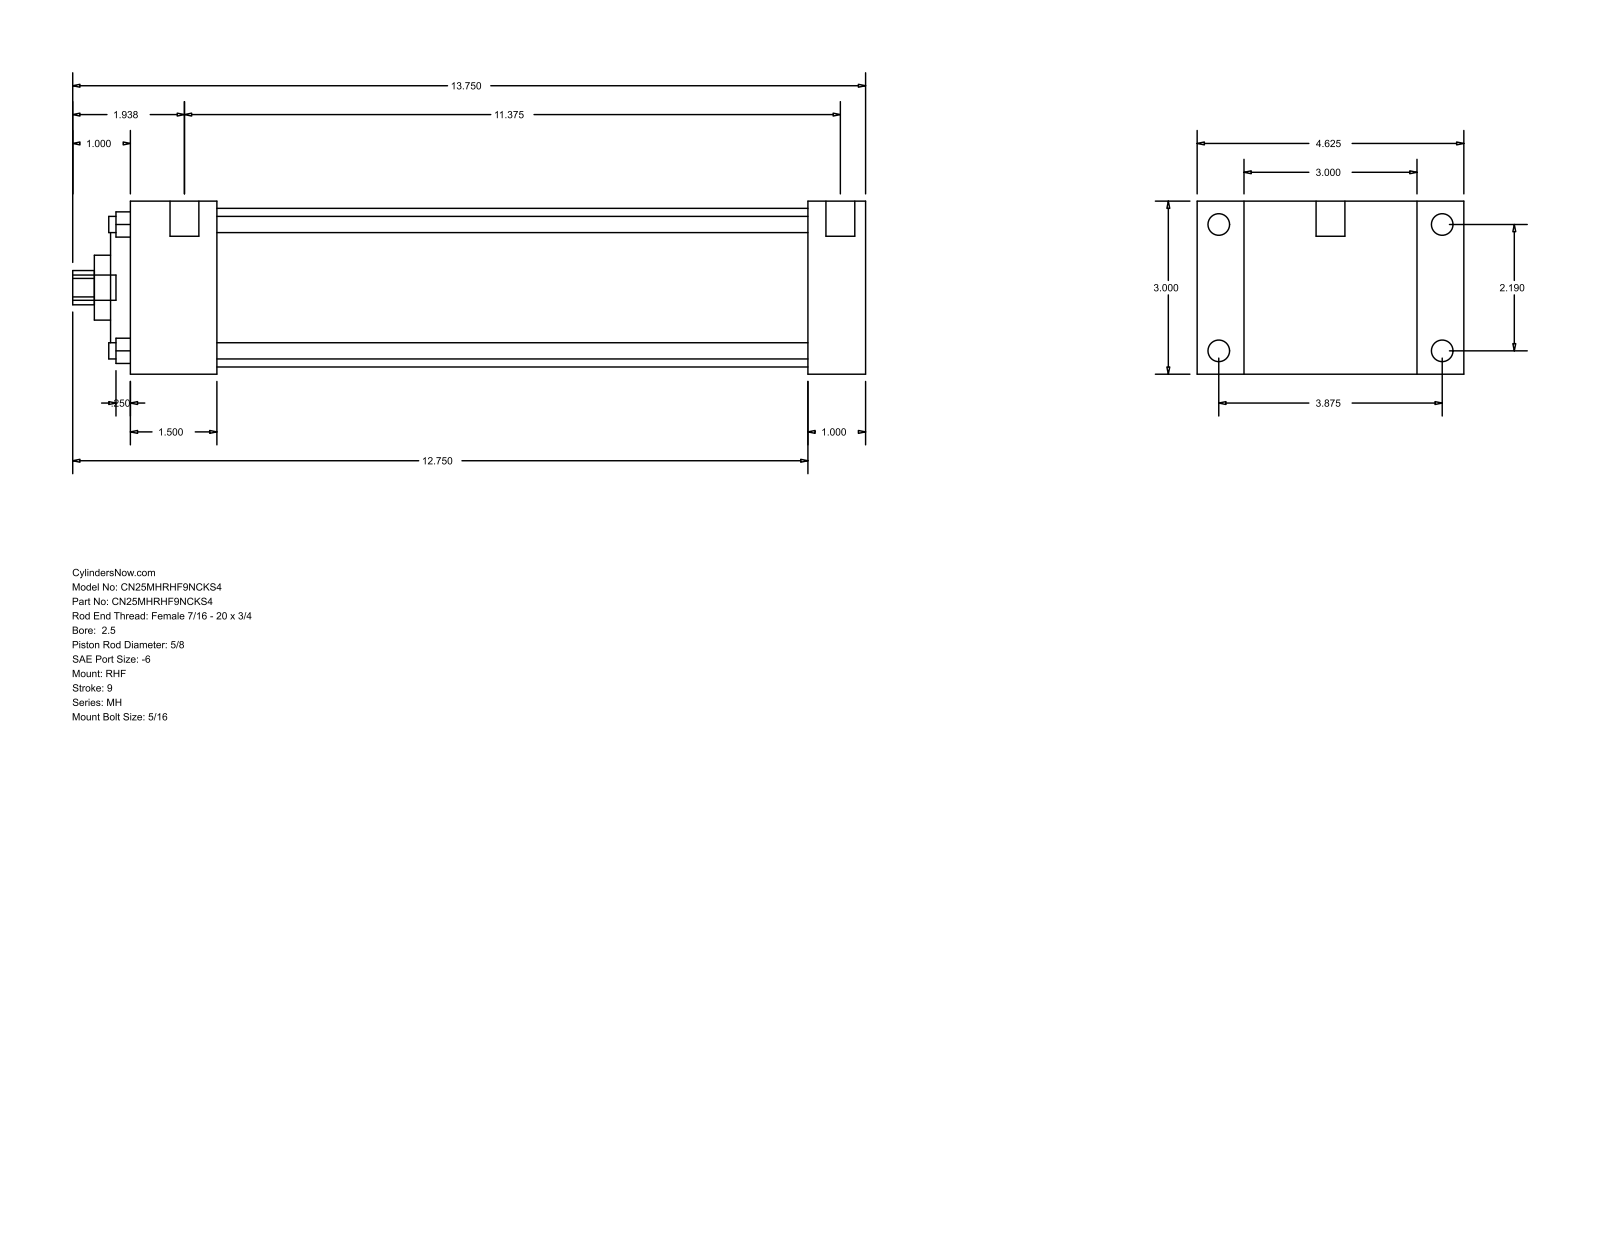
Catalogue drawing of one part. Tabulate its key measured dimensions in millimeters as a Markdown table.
| quantity | value |
| --- | --- |
| part name | MH_RHF__0250_0.625 |
| STEP written by | GSSL Pune (CONFIG_CONTROL_DESIGN) |
| units | millimeters |
| bodies | 0 solids, 90 faces (61 planar, 29 cylindrical, 0 other) |
| overall size | 349.25 × 117.47 × 76.2 |
| round holes (diameter × count) | 7.14 × 4, 15.88 × 1, 28.57 × 1, 55.55 × 1, 69.85 × 1 |
| round bosses / shafts (diameter × count) | 9.53 × 4, 5.56 × 4, 12.7 × 2, 11.11 × 1 |
| partial cylindrical surfaces (radius × count) | 7.54 × 1 |
| main face-to-face distances | 76.2, 25.4, 20.64, 96.84, 323.85, 298.45, 117.48, 38.1, 260.35, 285.75 |
| hole center spacings | 39.33, 55.62, 78.66 |
